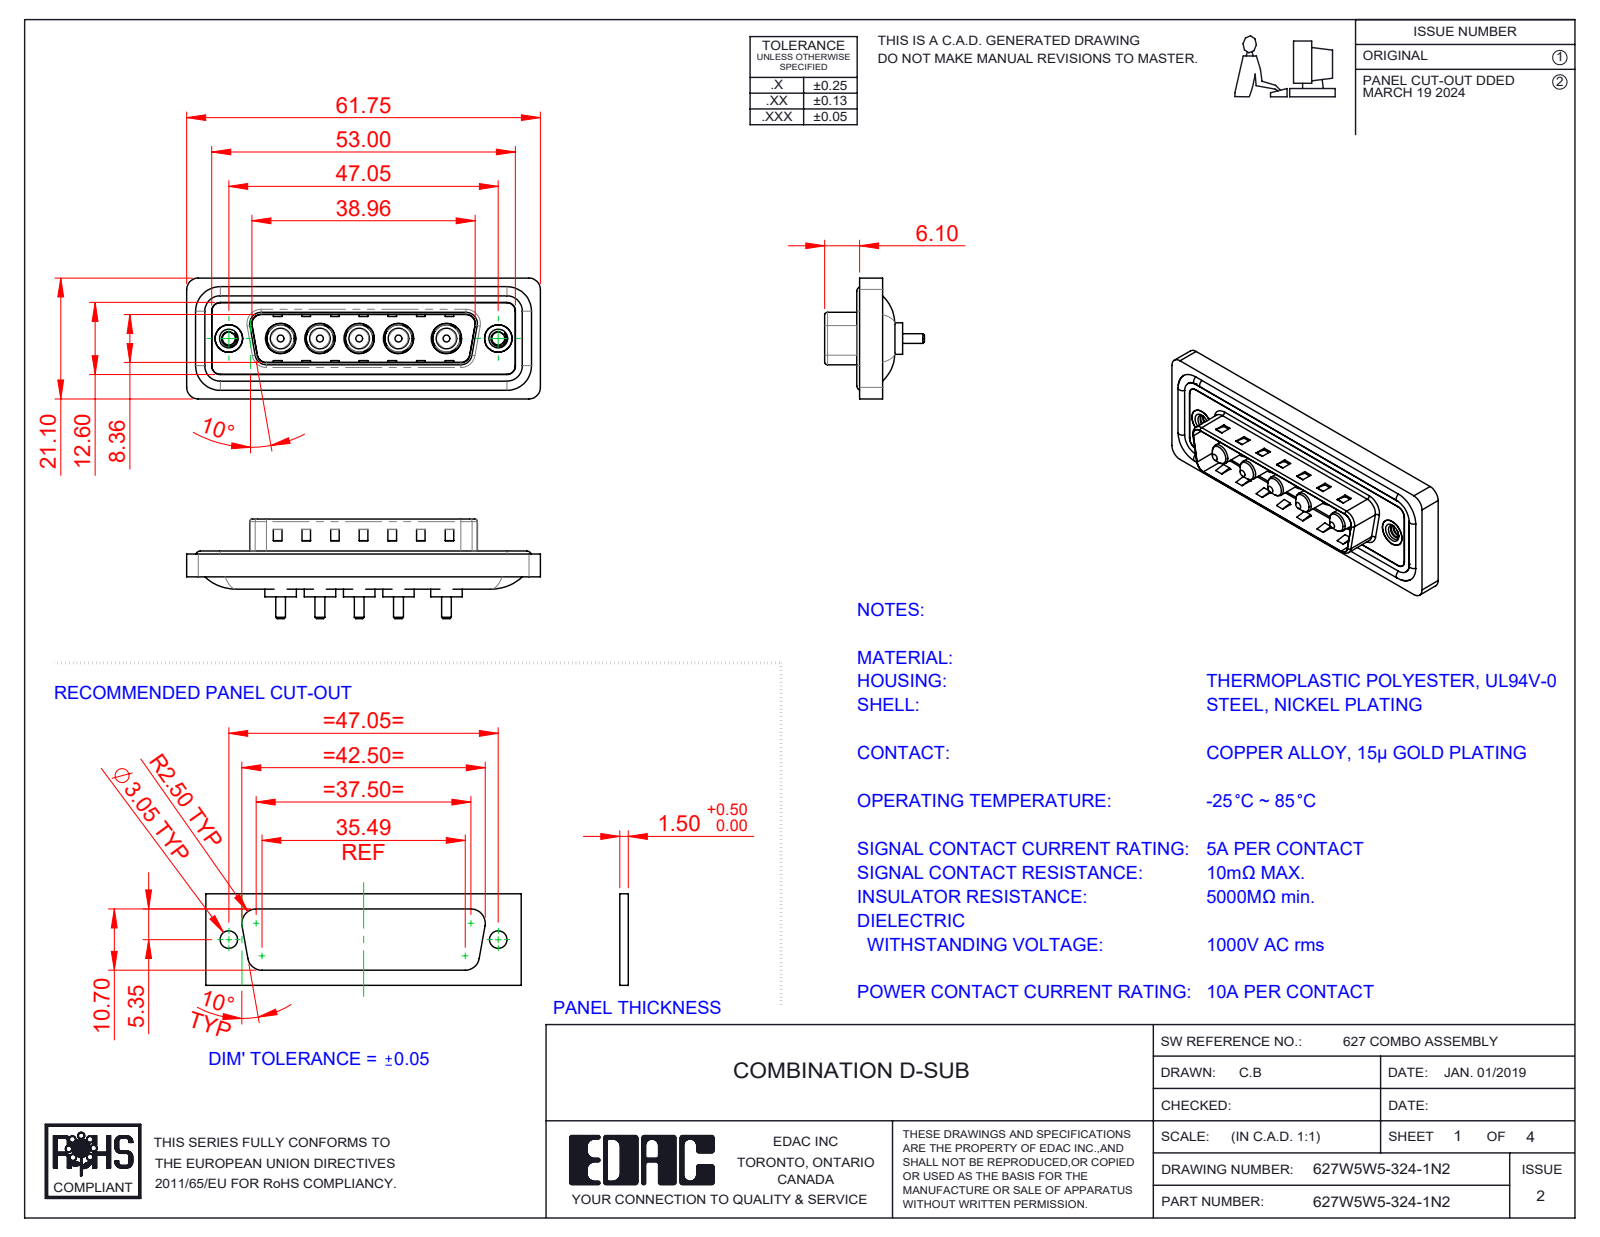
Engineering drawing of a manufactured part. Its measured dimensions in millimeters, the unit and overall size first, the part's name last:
Units: millimetres
Overall size (bounding box): 61.75 × 21.1 × 17.4
Round holes (diameter × count): ⌀4.85 ×5, ⌀5.3 ×5, ⌀2.26 ×2, ⌀4 ×2, ⌀4.8 ×2, ⌀5 ×2
Round bosses / shafts (diameter × count): ⌀5.5 ×5, ⌀5.2 ×5, ⌀4.75 ×5, ⌀3.75 ×5, ⌀3.6 ×5, ⌀1.7 ×5, ⌀1.6 ×4, ⌀4.9 ×2
Partial cylindrical surfaces — rounded edges, fillets, slot ends (radius × count): R1.5 ×22, R2 ×18, R0.5 ×8, R1.6 ×8, R2.1 ×5, R0.25 ×4, R0.6 ×4, R0.65 ×4
Main face-to-face distances: 0.4, 1.5, 0.5, 1.1, 3.1, 1.6, 2.9, 0.82, 9.58, 5.65
Hole centre spacings: 6.86, 9.04, 13.73, 38.01, 6.87, 8.37, 8.38, 9.05
Volume: 7 399 mm³ · Surface area: 11 733 mm²
Bodies: 17 solids, 678 faces (259 planar, 283 cylindrical, 136 other)
Part name (STEP PRODUCT): 627Combo Shell Rear_25 Contacts; 627Combo Threaded Rivet_2; 627Combo Housing_5W5; 627Combo Waterproof Housing_25 Contacts (+3 more)
STEP written by: SolidWorks 2023 (CONFIG_CONTROL_DESIGN)
